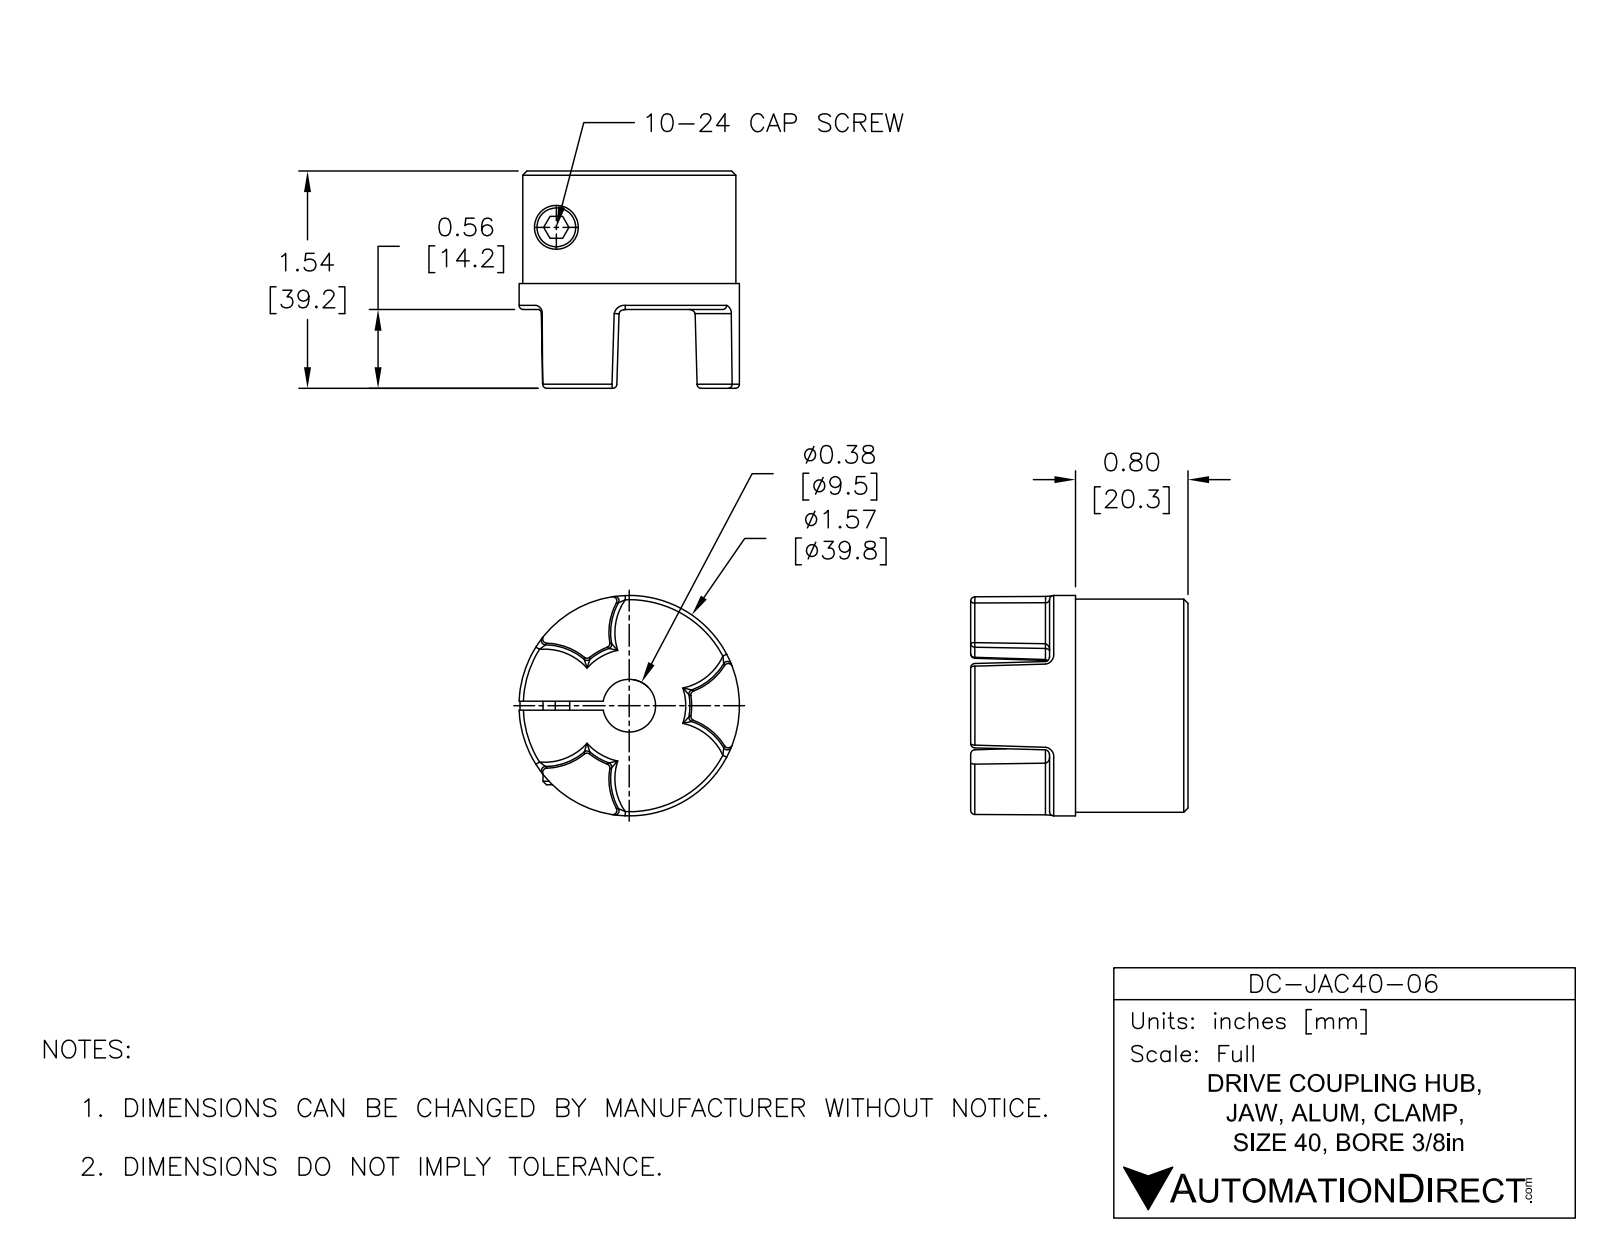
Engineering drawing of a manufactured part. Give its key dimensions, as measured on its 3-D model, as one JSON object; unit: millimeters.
{"part_name": "DC-JAC40-06", "step_written_by": "SolidWorks 2015 (AUTOMOTIVE_DESIGN)", "units": "millimeters", "bodies": {"solids": 1, "faces": 102, "planar": 12, "cylindrical": 15, "other": 75}, "overall_size": [39.78, 39.76, 39.22], "volume_mm3": 29950, "surface_area_mm2": 8660, "round_holes": [[5.11, 1], [8.36, 1], [9.53, 1]], "round_bosses_or_shafts": [[39.78, 1], [38.48, 1]], "face_to_face_distances": [24.99, 1.6, 39.22, 14.23, 20.29, 4.7, 18.93, 3.99, 5.59]}
